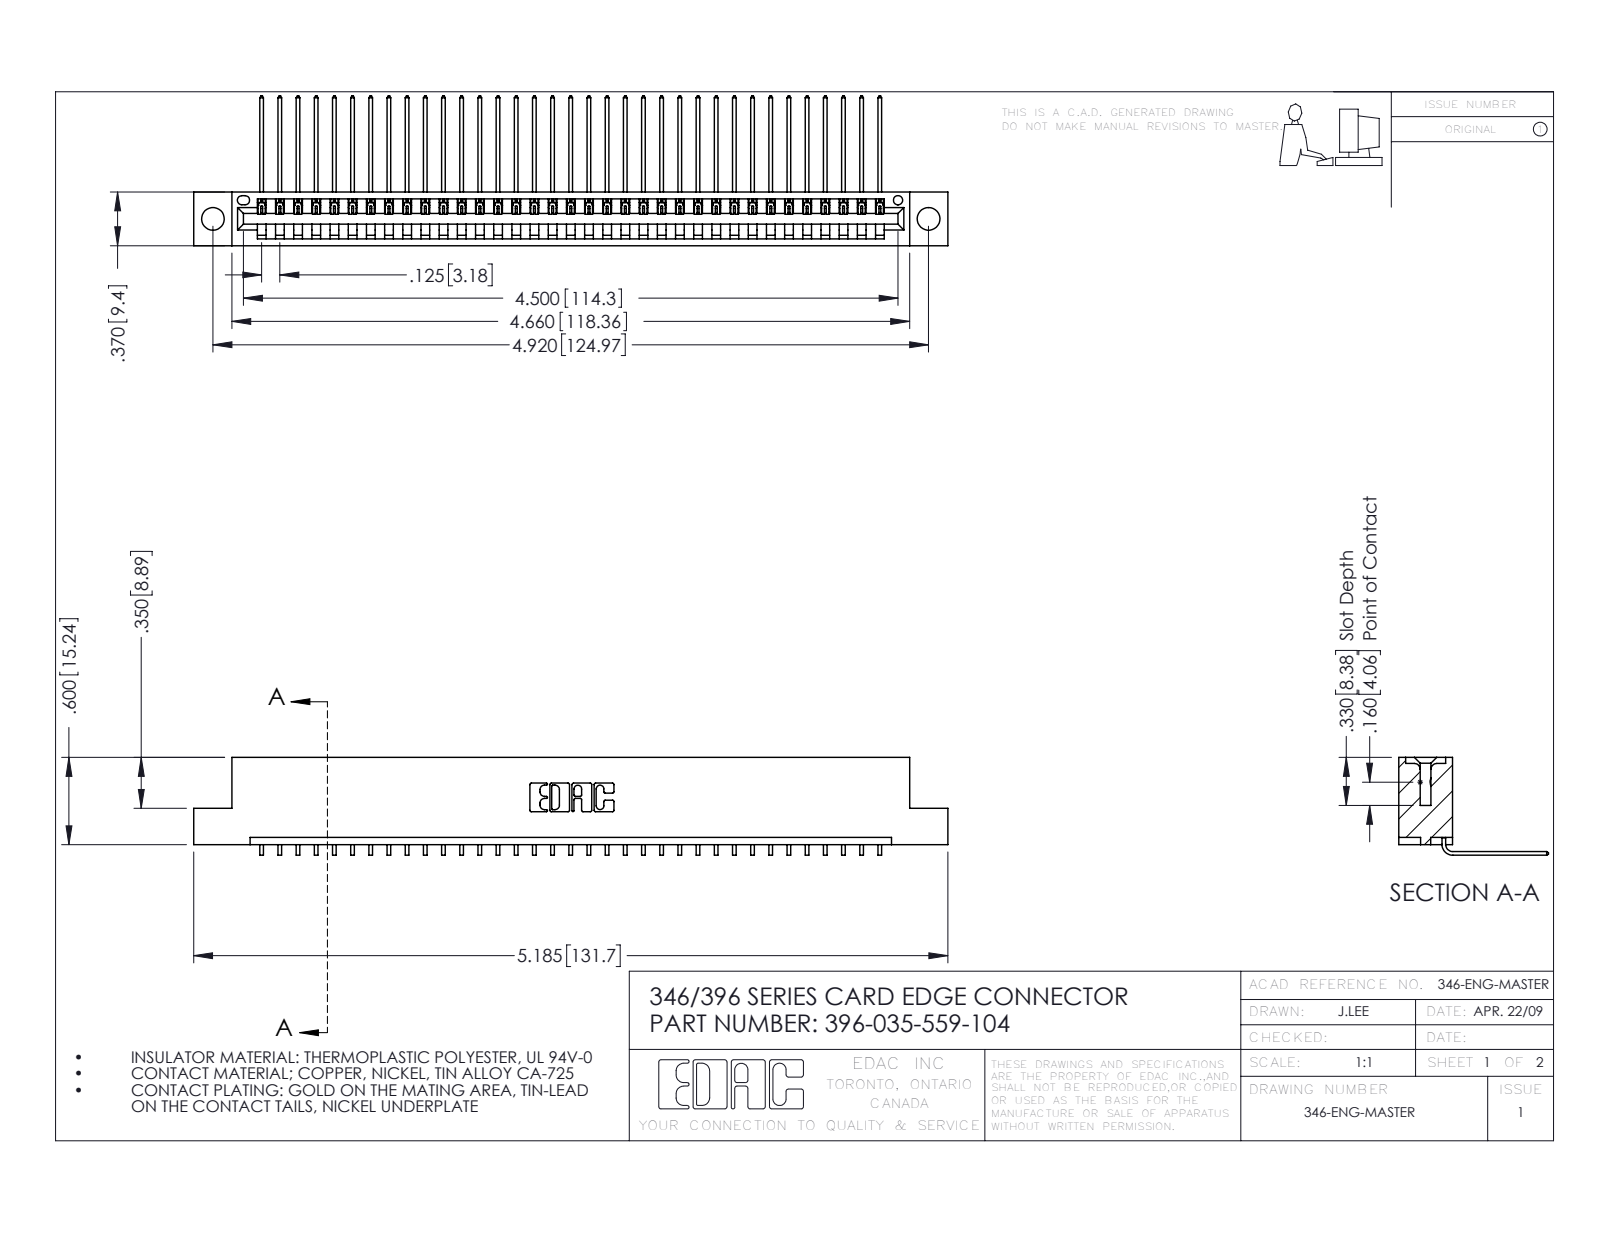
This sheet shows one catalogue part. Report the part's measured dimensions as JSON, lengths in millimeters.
{"part_name": "345-292-001_558 559 Tail - 1; 396-035-559-104; 346 Part_Flush Mounting Lugs - 0.156 Dia-TH", "step_written_by": "SolidWorks 2016 (CONFIG_CONTROL_DESIGN)", "units": "millimeters", "bodies": {"solids": 36, "faces": 2222, "planar": 1546, "cylindrical": 676, "other": 0}, "overall_size": [131.7, 26.2, 17.1], "volume_mm3": 12600, "surface_area_mm2": 16150, "round_holes": [[4, 2], [1.6, 1]], "partial_cylinders_radius": [[0.2, 70], [0.3, 22], [0.2, 6], [0.8, 6], [0.7, 3], [0.8, 2], [1, 2], [0.4, 1]], "face_to_face_distances": [1.2, 8.2, 9.4, 6.4, 0.6, 1.8, 7.6, 3.8, 5.6, 2.5], "hole_center_spacings": [6.2, 119.7, 125]}
